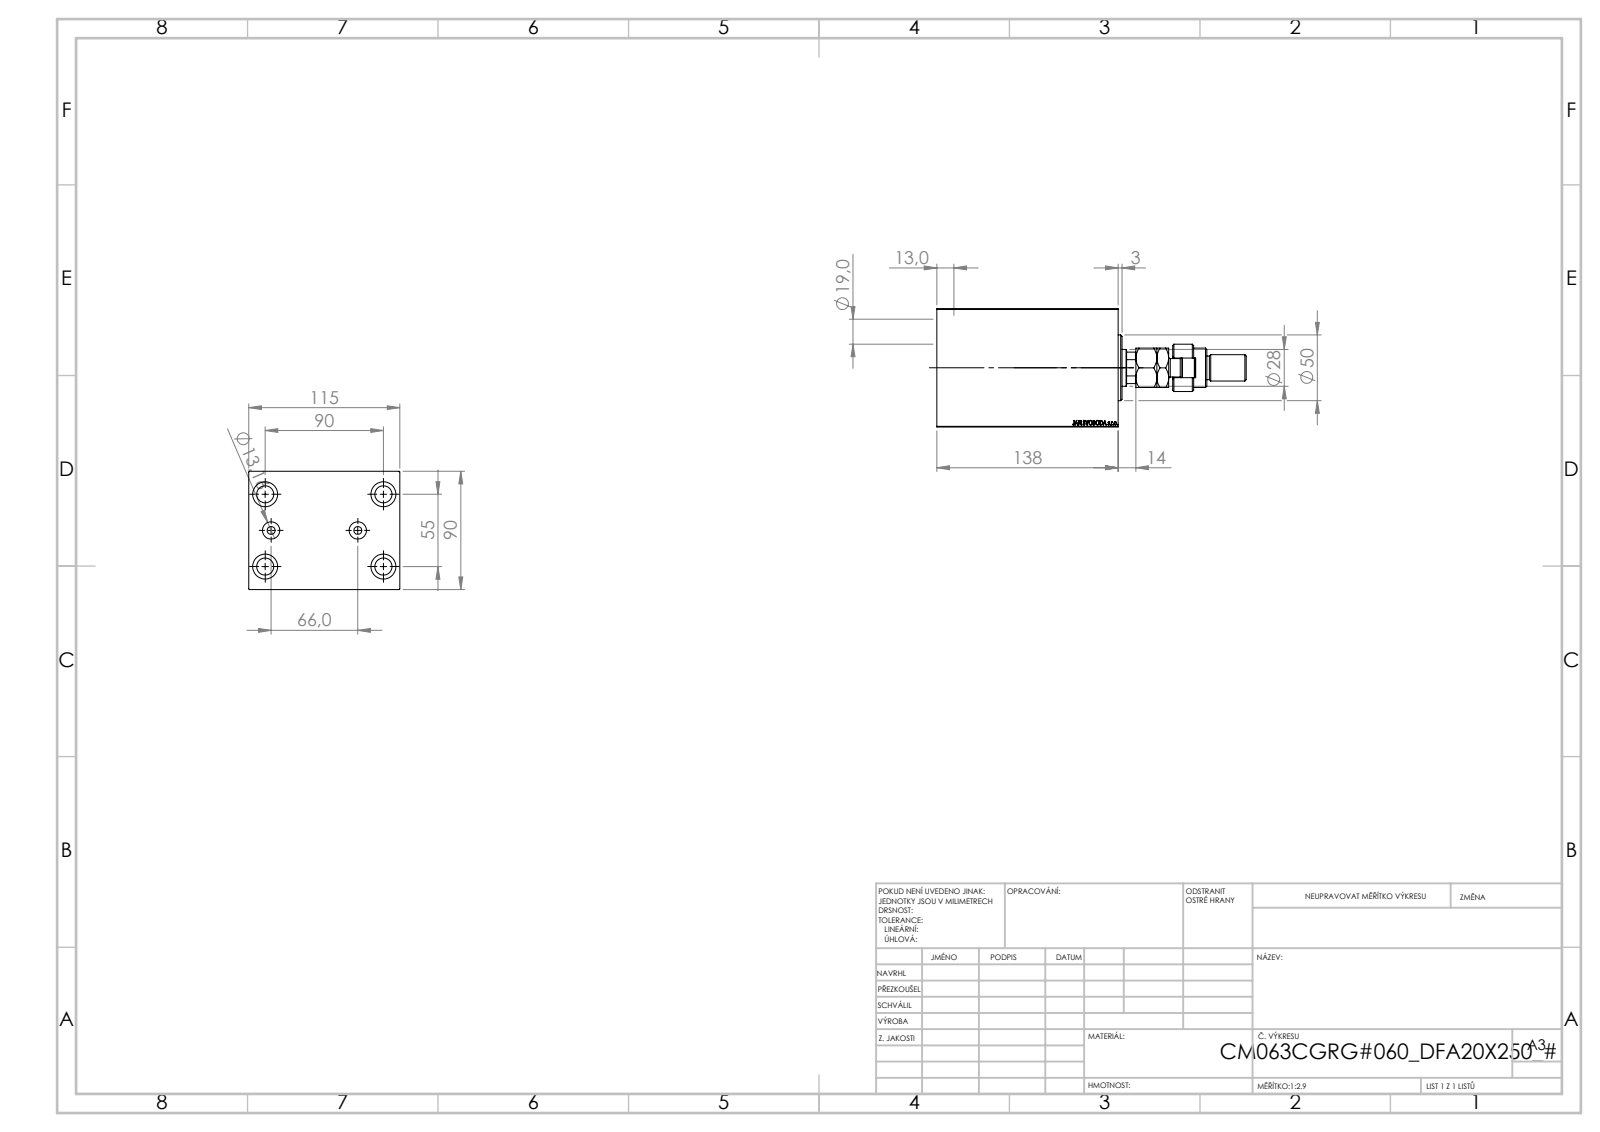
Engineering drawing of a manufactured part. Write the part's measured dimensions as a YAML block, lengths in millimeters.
part_name: "MFA; V450CM_C_Body; V450CM_VC_B; FEMALE_PART_FOR_DFA (+1 more)"
step_written_by: "SolidWorks 2019 (CONFIG_CONTROL_DESIGN)"
units: millimeters
bodies: {solids: 5, faces: 946, planar: 437, cylindrical: 71, other: 438}
overall_size: [235.5, 115, 90]
volume: 1234000
surface_area: 179719
round_holes:
  - {diameter: 13, count: 4}
  - {diameter: 19, count: 4}
  - {diameter: 6, count: 2}
  - {diameter: 13.16, count: 2}
  - {diameter: 18.5, count: 1}
  - {diameter: 28, count: 1}
  - {diameter: 31.5, count: 1}
  - {diameter: 63, count: 1}
  - {diameter: 65, count: 1}
  - {diameter: 72, count: 1}
round_bosses_or_shafts:
  - {diameter: 50, count: 1}
  - {diameter: 36, count: 1}
  - {diameter: 30, count: 1}
  - {diameter: 22, count: 1}
  - {diameter: 20, count: 1}
  - {diameter: 18, count: 1}
  - {diameter: 14, count: 1}
partial_cylinders:
  - {radius: 7.5, count: 1}
  - {radius: 12, count: 1}
  - {radius: 13.5, count: 1}
face_to_face_distances: [90, 115, 138, 17.5, 120.5, 60, 29.3, 91.2, 108.7, 89.3]
hole_center_spacings: [30, 52.74, 82.71, 33, 55, 90, 105.48, 66]
